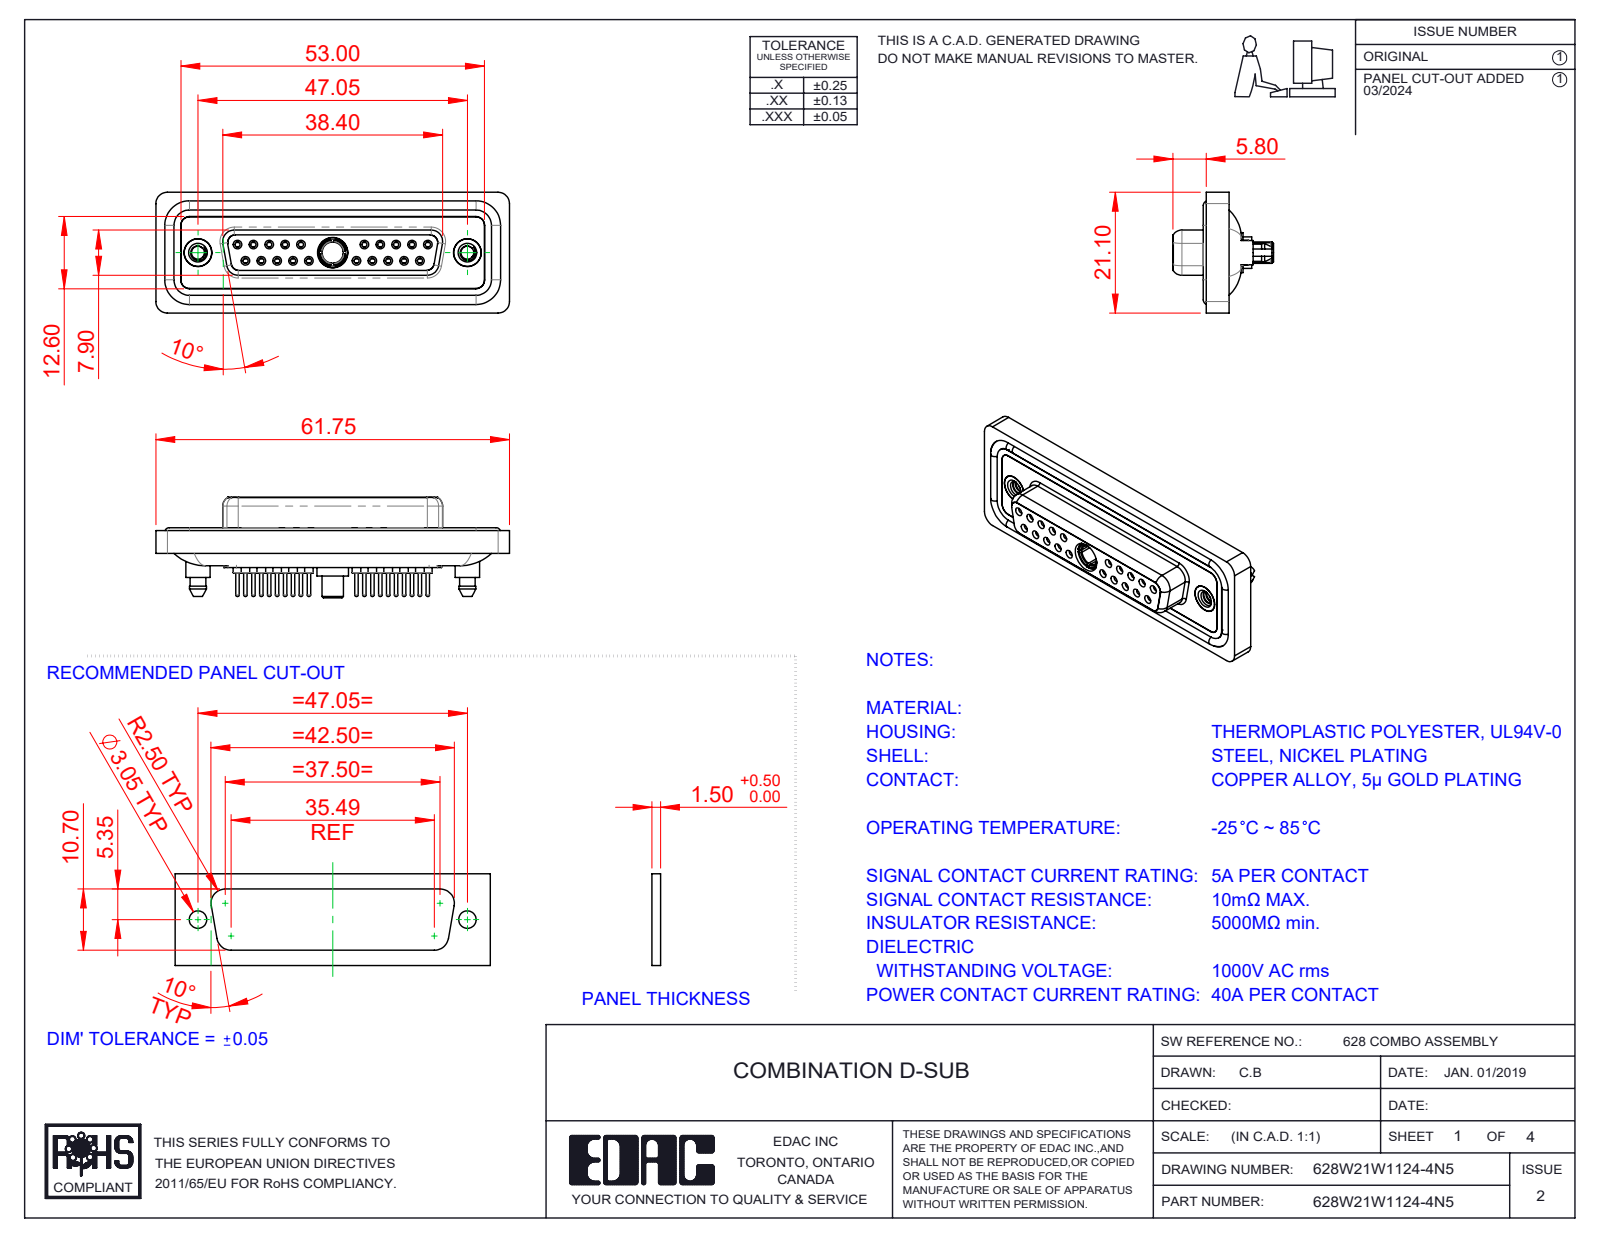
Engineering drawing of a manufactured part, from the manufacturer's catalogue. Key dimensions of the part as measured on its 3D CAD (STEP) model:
Part name (STEP PRODUCT): 628Combo Waterproof Housing_25 Contacts; 628Combo Shell Front_25 Contacts; 628Combo Contact Row 1_24; 628Combo Threaded Boardlock_5 (+5 more)
STEP written by: SolidWorks 2023 (CONFIG_CONTROL_DESIGN)
Units: millimetres
Bodies: 29 solids, 1610 faces (450 planar, 623 cylindrical, 537 other)
Overall size (bounding box): 61.75 × 21.1 × 17.55
Volume: 8 526 mm³ · Surface area: 14 346 mm²
Round holes (diameter × count): ⌀0.9 ×20, ⌀1.1 ×20, ⌀1.5 ×20, ⌀2 ×20, ⌀1.6 ×10, ⌀1.7 ×10, ⌀4.85 ×3, ⌀2.26 ×2, ⌀4 ×2, ⌀4.05 ×2, ⌀5 ×2, ⌀3.7 ×1
Round bosses / shafts (diameter × count): ⌀2.2 ×20, ⌀0.6 ×20, ⌀1.6 ×14, ⌀5.4 ×2, ⌀4.95 ×2, ⌀4.8 ×2, ⌀4.25 ×2, ⌀5.5 ×1
Partial cylindrical surfaces — rounded edges, fillets, slot ends (radius × count): R1.5 ×24, R2 ×18, R1.6 ×10, R1.35 ×8, R0.25 ×4, R0.5 ×4, R0.6 ×4, R0.65 ×4
Main face-to-face distances: 0.4, 1.8, 7.45, 6.6, 5.65, 1.6, 0.5, 7.05, 2.9, 1.1
Hole centre spacings: 3.16, 2.77, 5.54, 5.03, 8.31, 7.48, 16.62, 19.39
